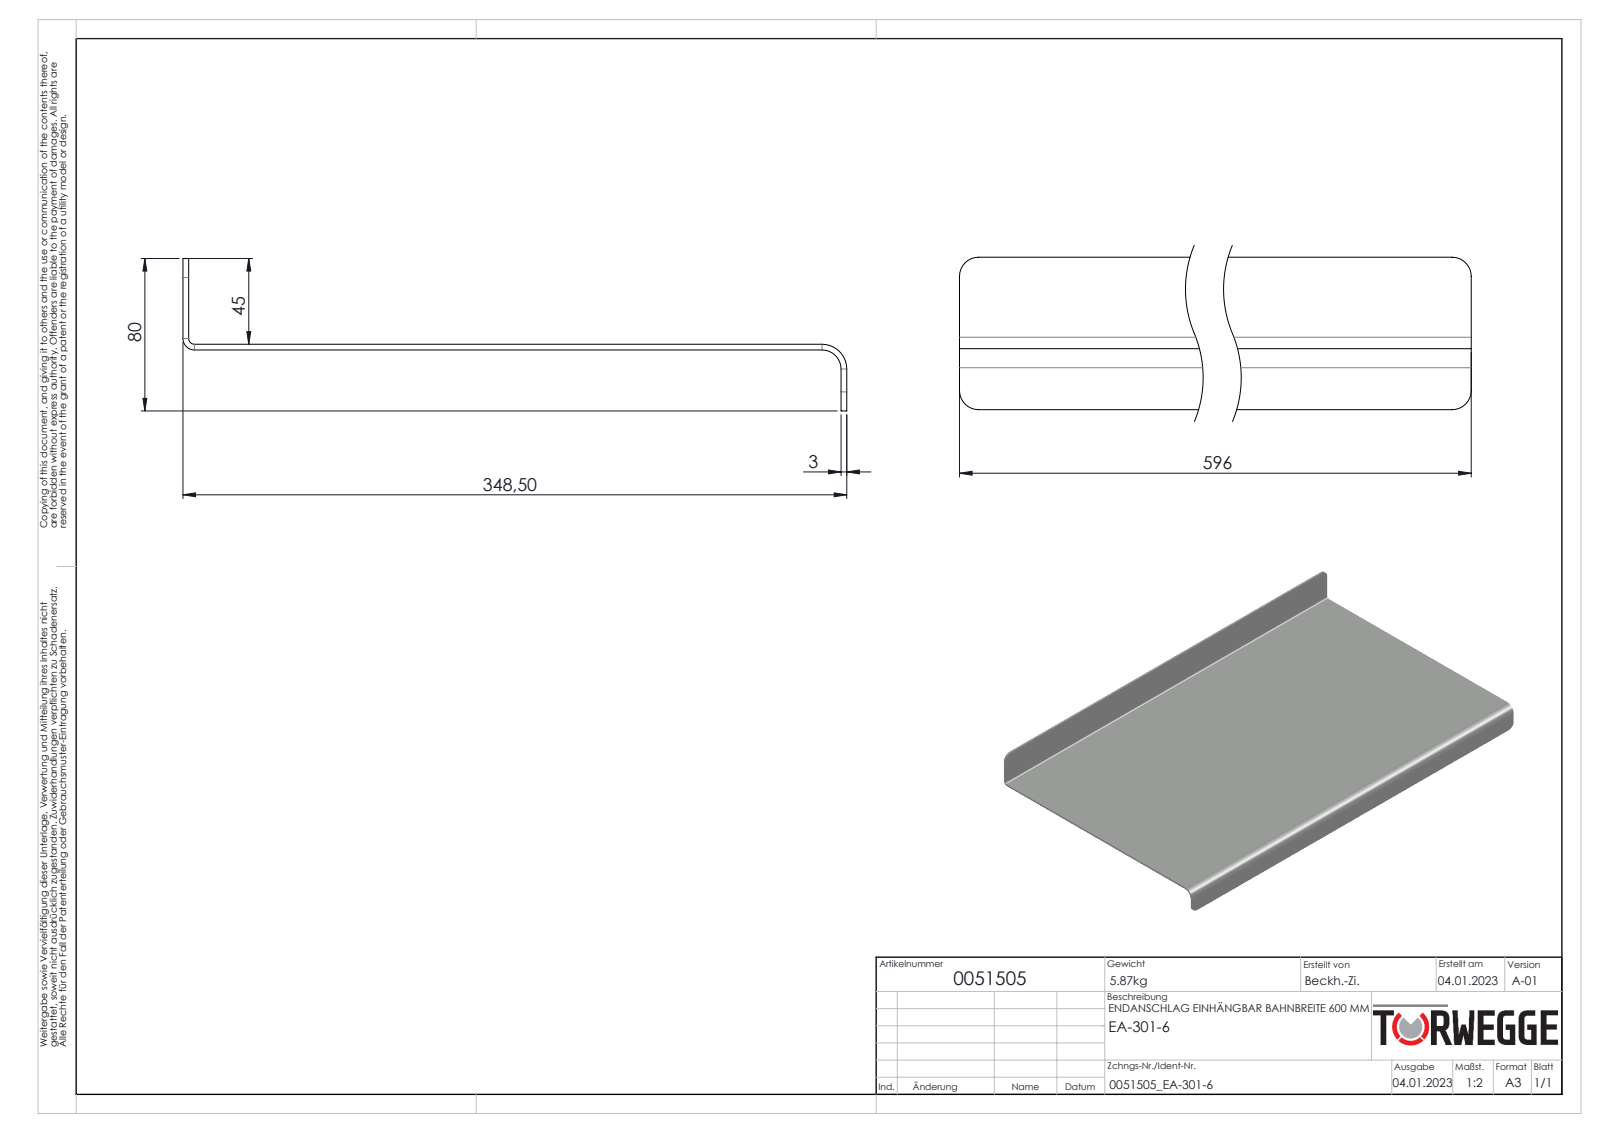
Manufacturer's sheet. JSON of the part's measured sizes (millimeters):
{"part_name": "0051505", "step_written_by": "SolidWorks 2020 (AUTOMOTIVE_DESIGN)", "units": "millimeters", "bodies": {"solids": 1, "faces": 26, "planar": 18, "cylindrical": 8, "other": 0}, "overall_size": [596, 348.5, 80], "volume_mm3": 748258, "surface_area_mm2": 504875, "partial_cylinders_radius": [[10, 5], [3, 1], [6, 1], [13, 1]], "face_to_face_distances": [3, 345.5, 342.5, 348.5, 32, 35, 80, 48, 45, 596]}
